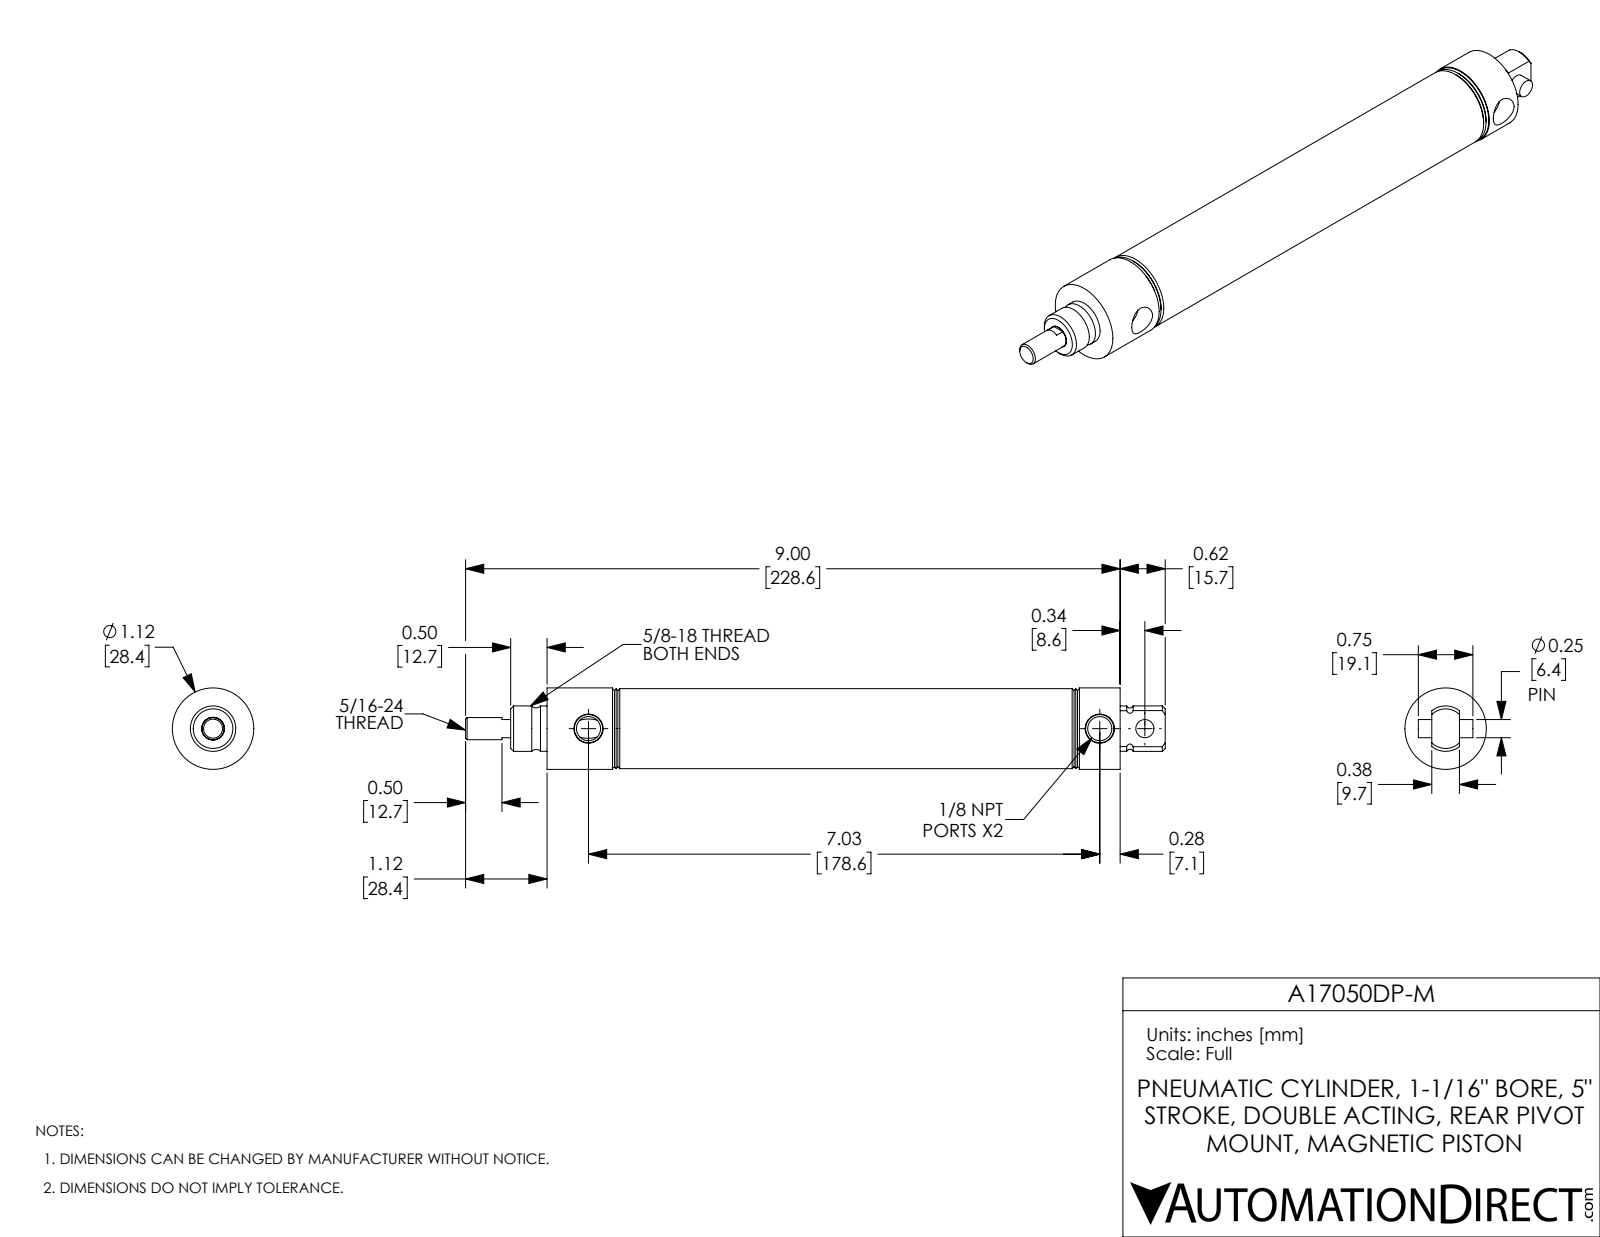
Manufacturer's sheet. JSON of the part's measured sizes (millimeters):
{"part_name": "A17050DP-M; A17050DP-M-PIN; A17050DP-M-Rod; A17050DP-M-MainBody", "step_written_by": "SolidWorks 2017 (AUTOMOTIVE_DESIGN)", "units": "millimeters", "bodies": {"solids": 3, "faces": 92, "planar": 22, "cylindrical": 32, "other": 38}, "overall_size": [244.3, 28.4, 28.4], "volume_mm3": 61070, "surface_area_mm2": 42340, "round_holes": [[8.4, 2], [6.4, 1], [7.9, 1], [27, 1]], "round_bosses_or_shafts": [[28.4, 1], [27.9, 1], [15.9, 1], [15.8, 1], [7.7, 1]], "partial_cylinders_radius": [[8, 1]], "face_to_face_distances": [12.7, 169.9, 139.7, 127, 30.2, 42.9, 169.9, 200.2, 157.2, 30.2], "hole_center_spacings": [15.7, 178.6, 194.3]}
